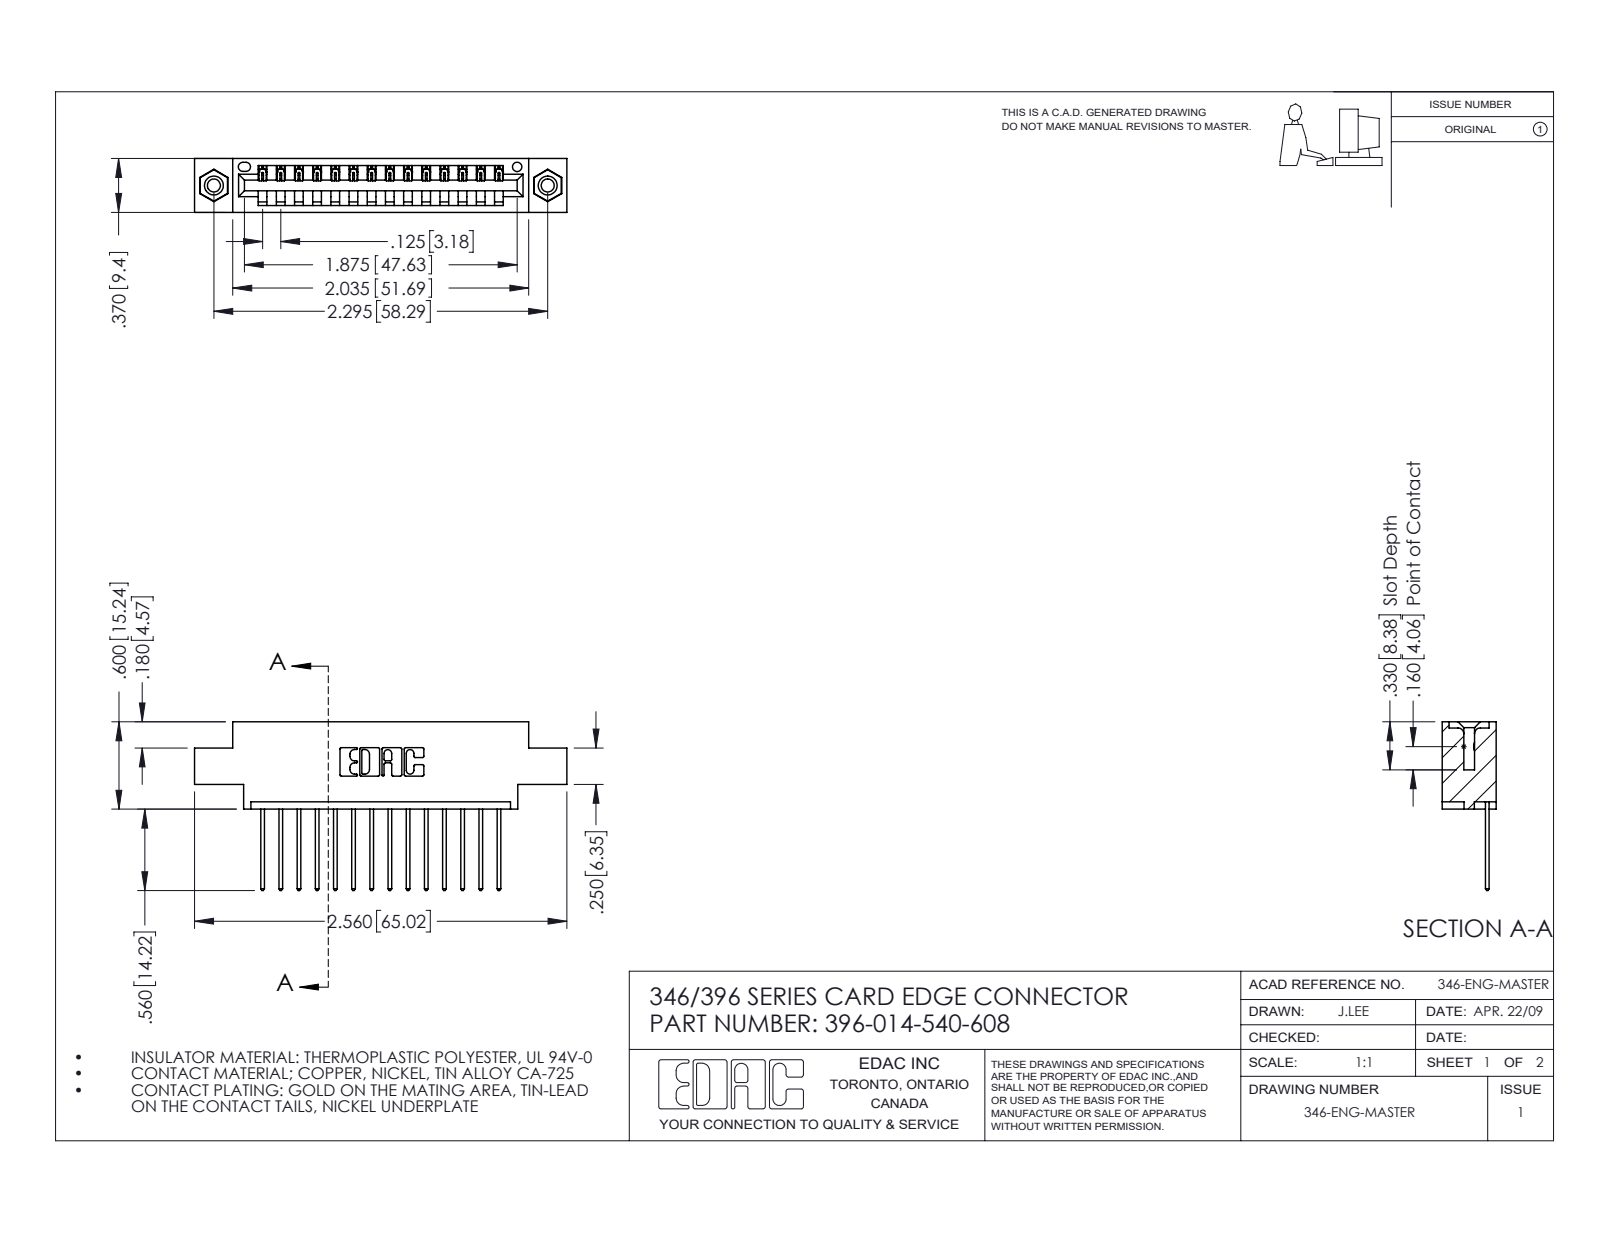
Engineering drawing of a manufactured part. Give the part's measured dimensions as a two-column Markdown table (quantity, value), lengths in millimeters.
| quantity | value |
| --- | --- |
| part name | 345-250-001_345-250-003-102; 346 Part_0.170 Offset - 0.156 Dia-TI; 396-014-540-608; 345-292-001_345-293-140 |
| STEP written by | SolidWorks 2016 (CONFIG_CONTROL_DESIGN) |
| units | millimeters |
| bodies | 17 solids, 998 faces (672 planar, 310 cylindrical, 16 other) |
| overall size | 65 × 29.5 × 9.4 |
| volume | 5 880 mm³ |
| surface area | 7 381 mm² |
| round holes (diameter × count) | 2.3 × 2, 3.2 × 2, 4 × 2, 1.6 × 1 |
| round bosses / shafts (diameter × count) | 3.9 × 2 |
| partial cylindrical surfaces (radius × count) | 0.2 × 28, 0.3 × 28, 0.3 × 22, 0.2 × 6, 0.8 × 6, 0.7 × 3, 0.8 × 2, 1 × 2 |
| main face-to-face distances | 1.2, 8.2, 9.4, 6.4, 1.8, 7.6, 0.6, 5.6, 3.8, 2.5 |
| hole center spacings | 6.2, 53.1, 58.3 |
